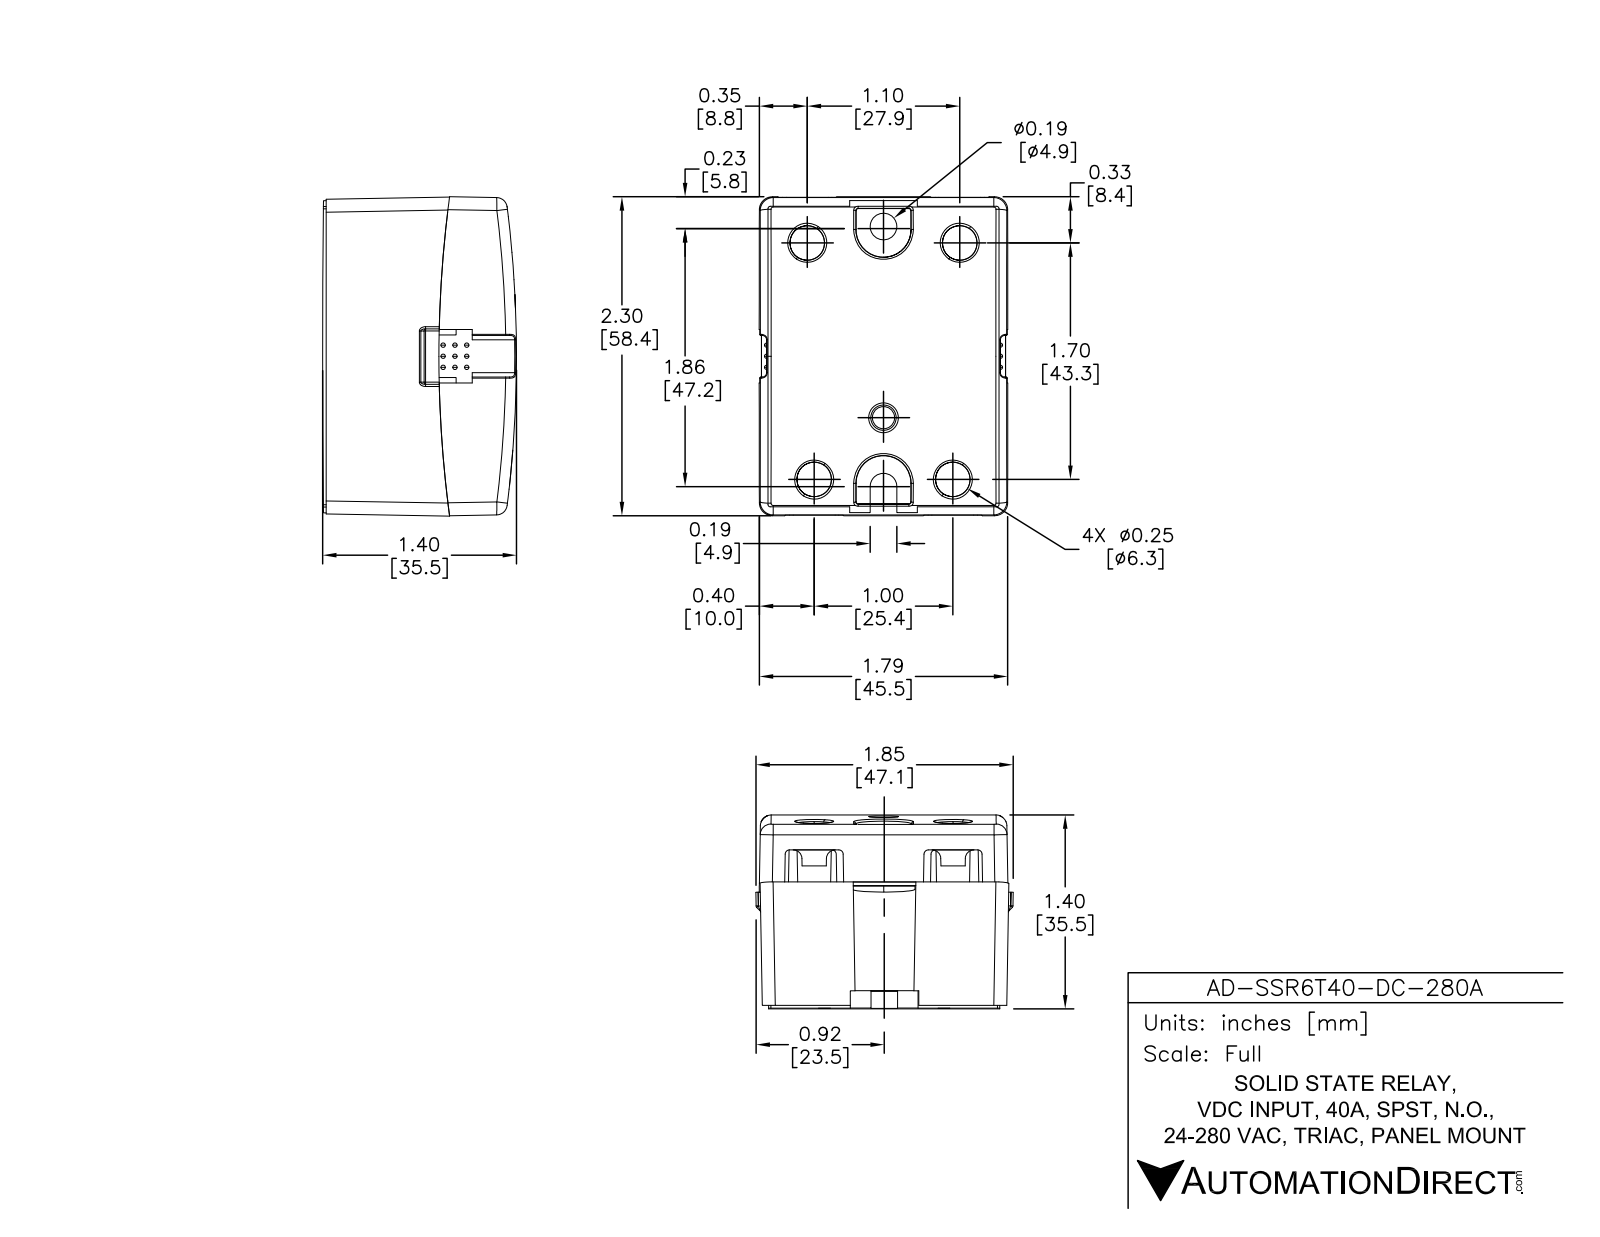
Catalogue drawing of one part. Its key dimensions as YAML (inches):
part_name: "AD-SSR6T40-DC-280A"
step_written_by: "SolidWorks 2013 (AUTOMOTIVE_DESIGN)"
units: inches
bodies: {solids: 3, faces: 251, planar: 145, cylindrical: 95, other: 11}
overall_size: [2.3, 1.79, 1.4]
volume: 5.14
surface_area: 26.41
round_holes:
  - {diameter: 0.25, count: 4}
  - {diameter: 0.19, count: 1}
round_bosses_or_shafts:
  - {diameter: 0.4, count: 2}
  - {diameter: 0.35, count: 2}
  - {diameter: 0.3, count: 2}
  - {diameter: 0.25, count: 2}
  - {diameter: 0.2, count: 2}
  - {diameter: 0.2, count: 2}
partial_cylinders:
  - {radius: 0.03, count: 6}
  - {radius: 0.01, count: 4}
  - {radius: 0.04, count: 4}
  - {radius: 0.5, count: 4}
  - {radius: 0.194, count: 2}
  - {radius: 0.095, count: 1}
  - {radius: 0.5, count: 1}
  - {radius: 0.5, count: 1}
face_to_face_distances: [1.79, 2.3, 1.166, 0.25, 0.916, 0.671, 1.059, 0.5, 1.8, 0.08]
hole_center_spacings: [0.556, 0.565, 1, 1.1, 1.7, 1.701, 1.876, 1.879]
